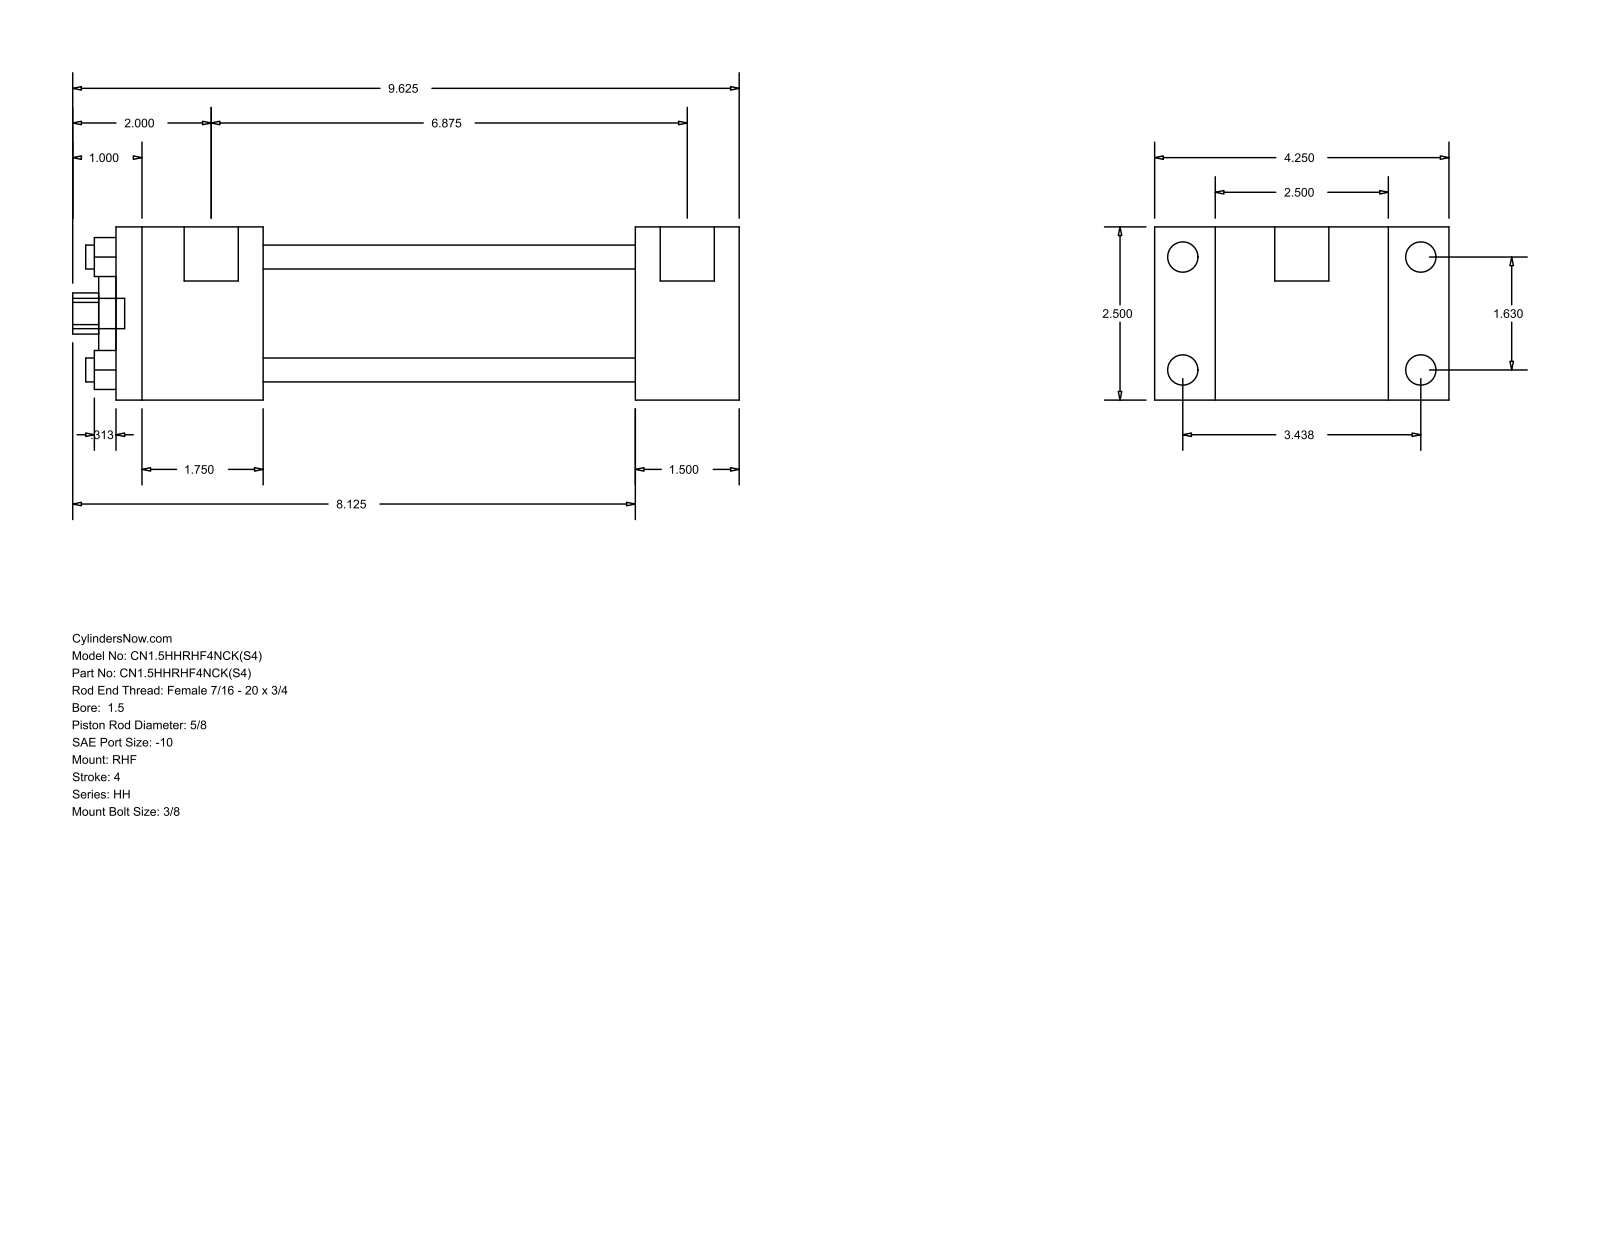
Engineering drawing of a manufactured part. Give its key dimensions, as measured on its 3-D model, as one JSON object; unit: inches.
{"part_name": "HH_RHF__0150_0.625", "step_written_by": "GSSL Pune (CONFIG_CONTROL_DESIGN)", "units": "inches", "bodies": {"solids": 0, "faces": 88, "planar": 60, "cylindrical": 28, "other": 0}, "overall_size": [9.625, 4.25, 2.5], "round_holes": [[0.345, 4], [0.625, 1], [1.125, 1], [1.75, 1]], "round_bosses_or_shafts": [[0.438, 4], [0.219, 4], [0.781, 2], [0.437, 1]], "partial_cylinders_radius": [[0.297, 1]], "face_to_face_distances": [2.5, 0.875, 3.375, 1.5, 7.5, 9, 4.25, 2.125, 5.375, 6.875], "hole_center_spacings": [1.152, 1.63, 2.305]}
